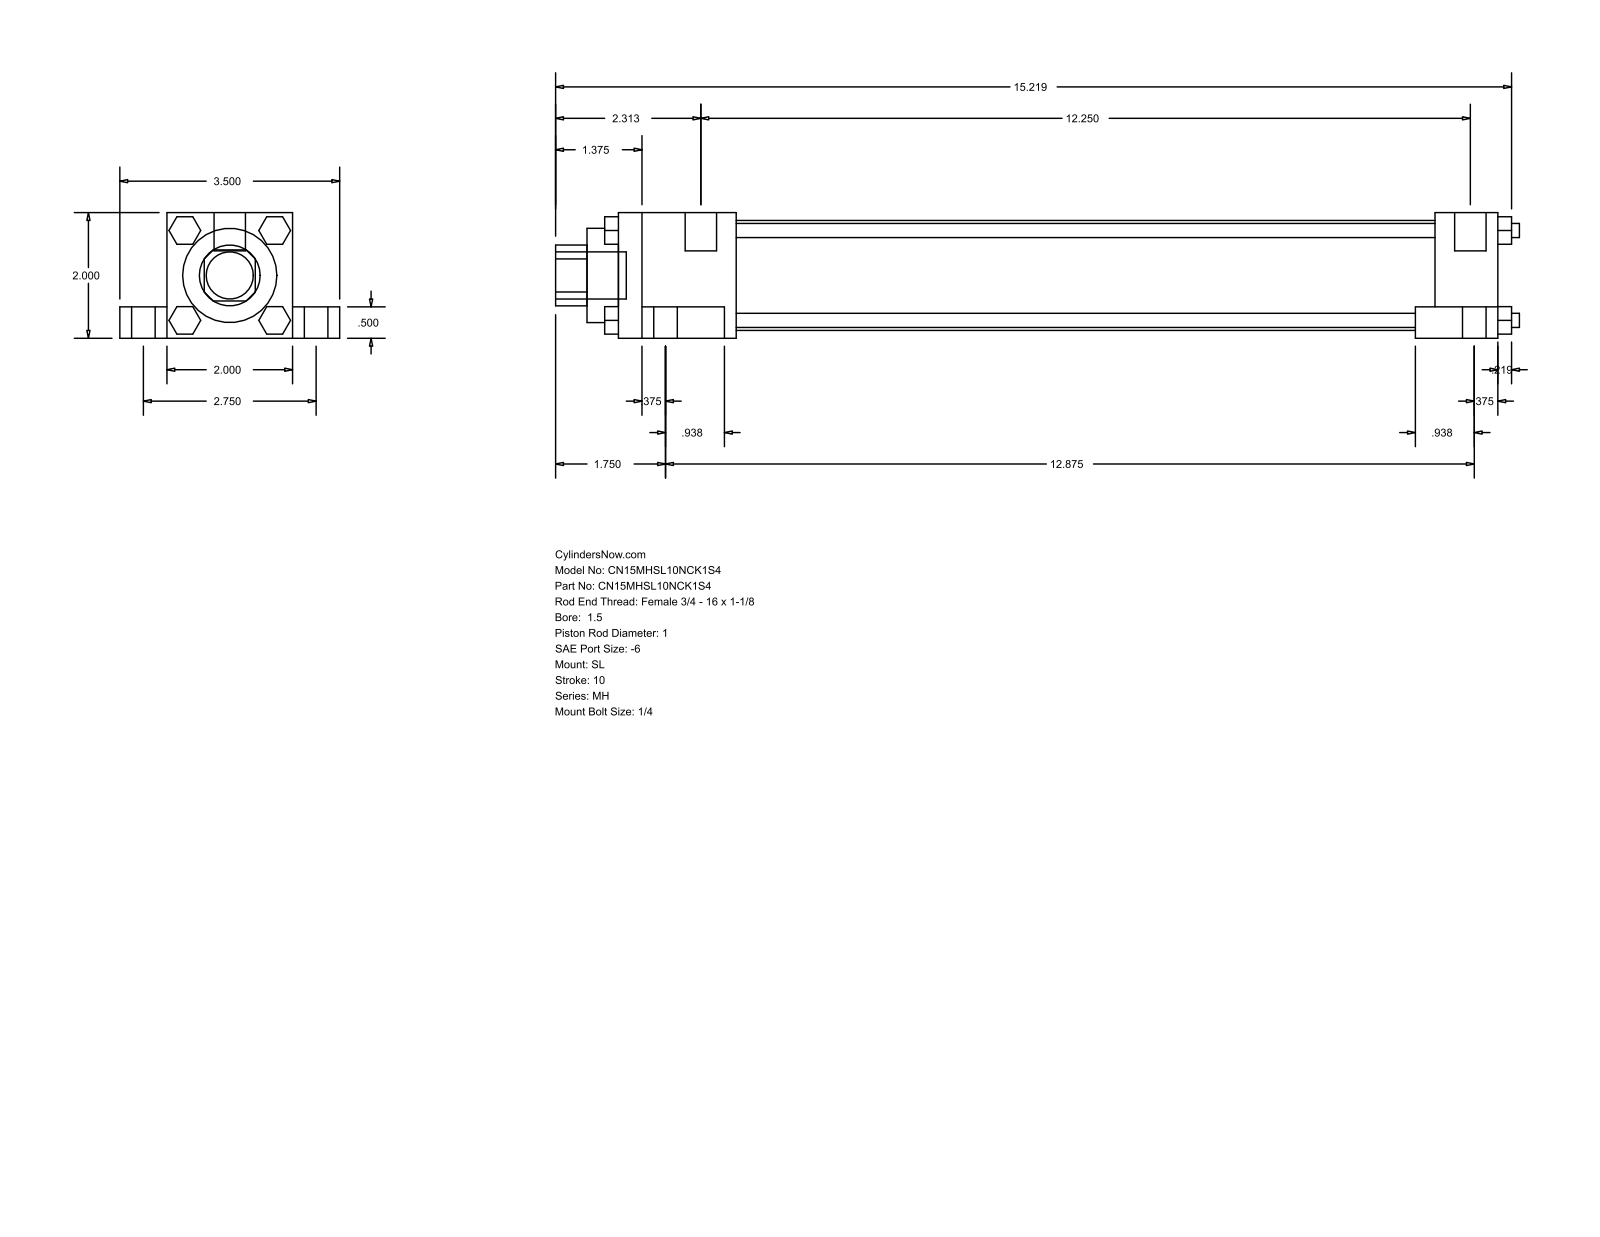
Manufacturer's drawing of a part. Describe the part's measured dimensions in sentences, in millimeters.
The part is named "MH_SL__0150_1". Its 3-D file was written by "GSSL Pune (CONFIG_CONTROL_DESIGN)". It is 0 solids with 148 faces: 112 planar, 36 cylindrical and 0 other. Overall it measures 389.73 by 88.9 by 50.8 millimeters. Round holes: 1 of diameter 25.4, 1 of diameter 38.1, 1 of diameter 44.45. Round bosses or shafts: 4 of diameter 15.88, 4 of diameter 9.53, 4 of diameter 5.71, 4 of diameter 5.56, 2 of diameter 12.7, 1 of diameter 19.05. Partial cylindrical surfaces (rounded edges, fillets, slot ends): 1 of radius 12.29. The main face-to-face distances are 50.8, 12.7, 38.1, 19.05, 69.85, 355.6, 25.4, 9.52, 33.34, 312.74.
